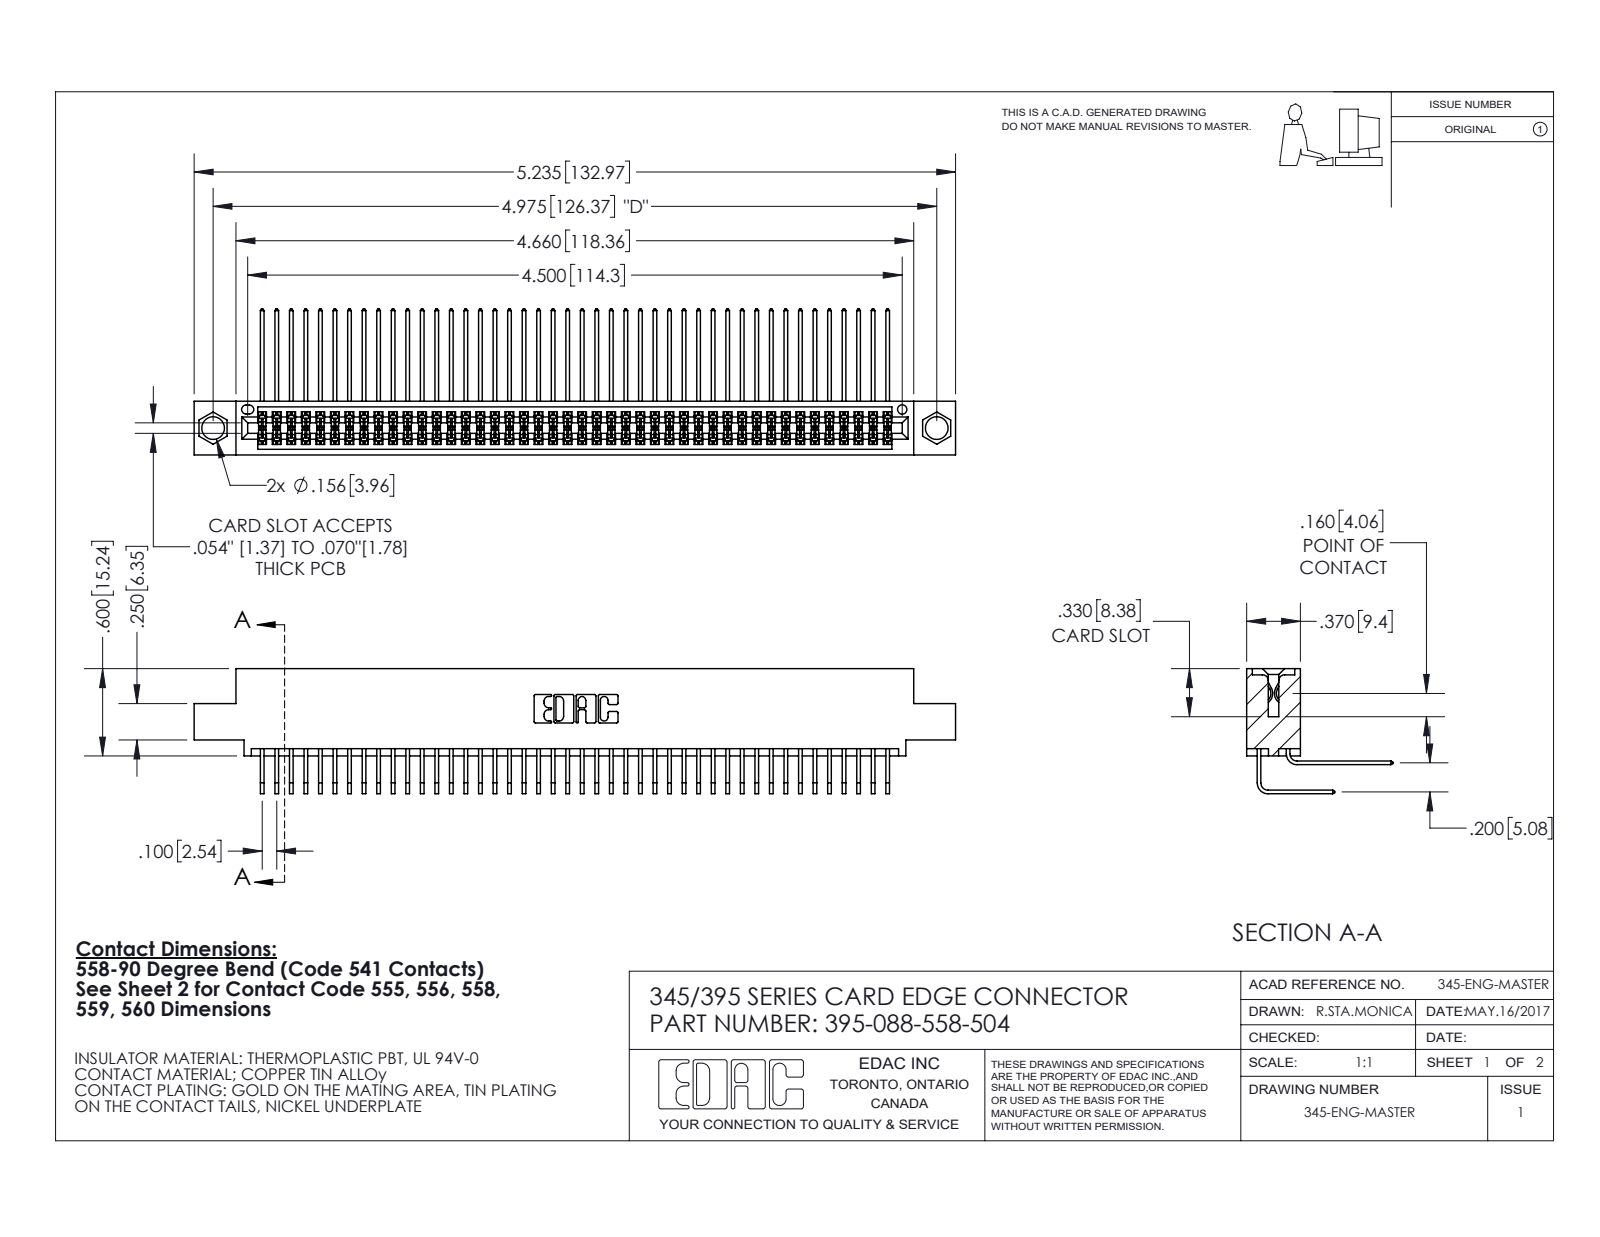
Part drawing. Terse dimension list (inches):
name: 345-292-001_558 Tail - 2; 345-292-001_558 559 Tail - 1; 395-088-558-504; 345 Part_0.110 Offset - 0.156 Dia-TI
written by: SolidWorks 2020 (CONFIG_CONTROL_DESIGN)
unit: in
bodies: 89 solids, 4720 faces (3178 planar, 1542 cylindrical, 0 other)
size: 5.235 × 1.005 × 0.859
volume: 0.809 in³; area: 34.06 in²
holes: 2× ⌀0.156, 1× ⌀0.064
rounds: 176× R0.006, 22× R0.01, 6× R0.007, 6× R0.031, 3× R0.026, 2× R0.014, 2× R0.019, 2× R0.022
face distances: 0.072, 0.298, 0.2, 0.37, 0.098, 0.272, 0.025, 0.225, 0.025, 0.175
hole spacings: 0.27, 4.739, 4.975
